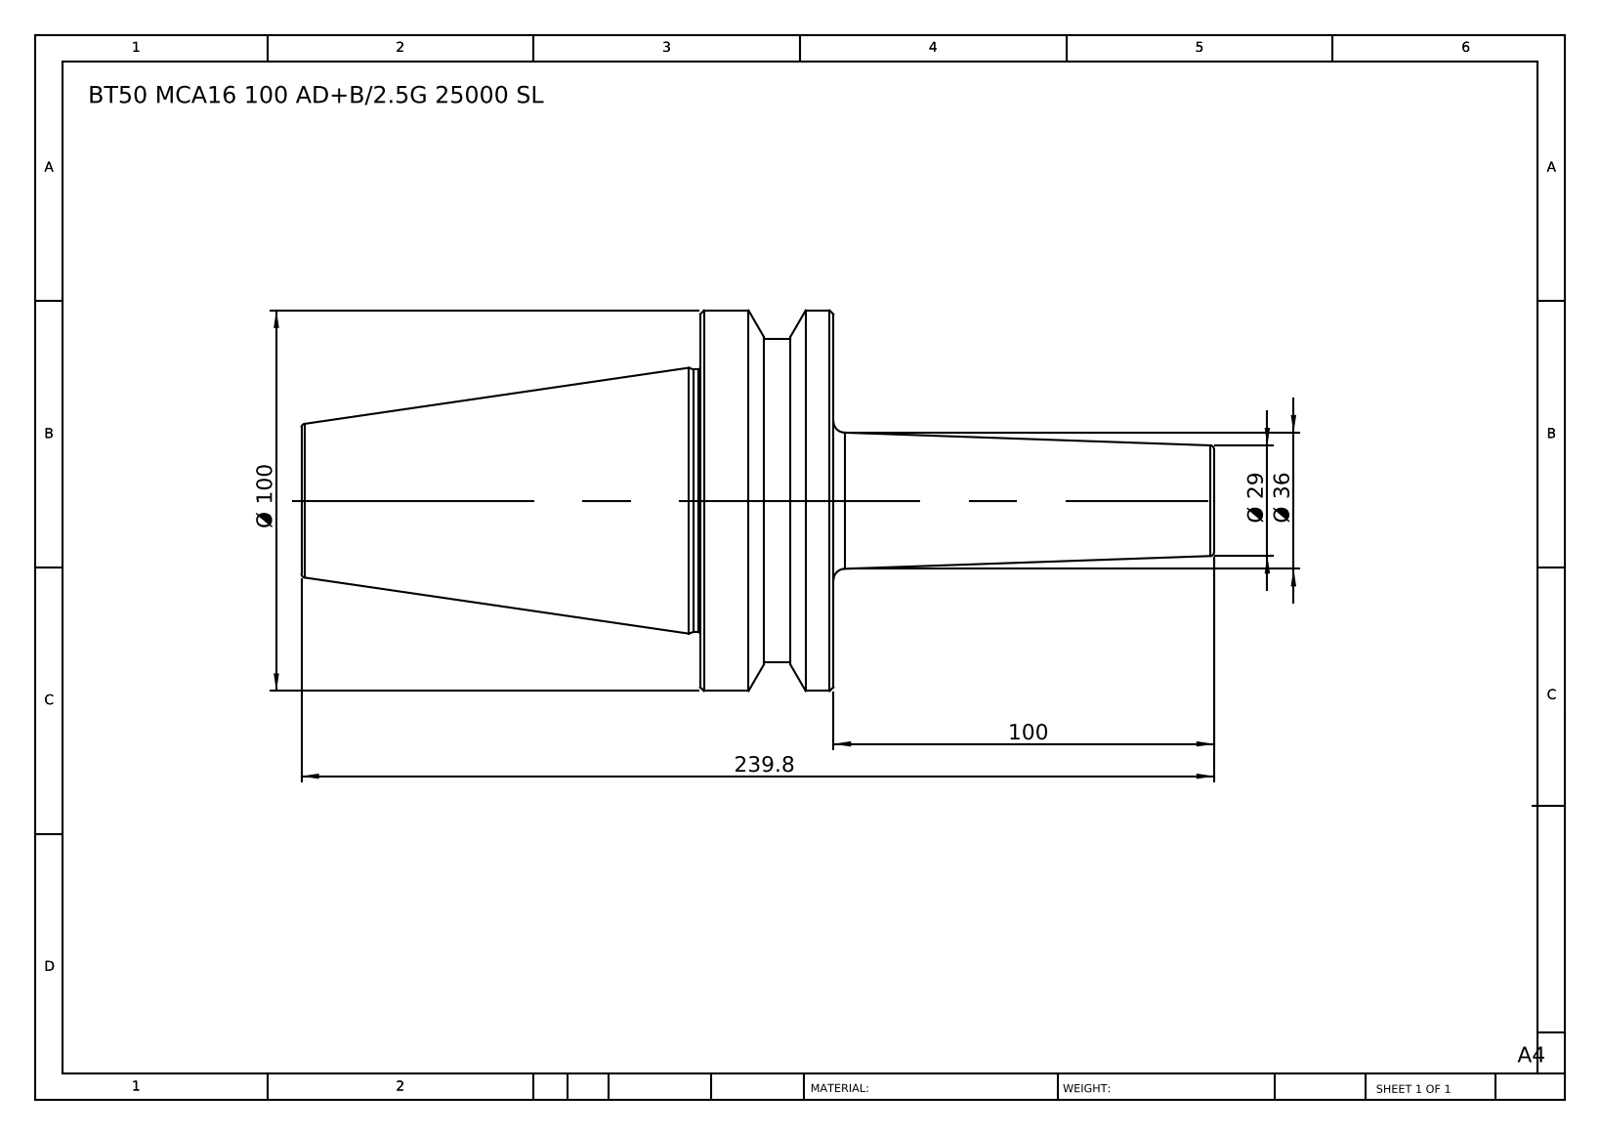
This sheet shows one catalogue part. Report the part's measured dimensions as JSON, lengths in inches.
{"part_name": "BT50 MCA16 100 AD+B-2.5G 25000 SL", "step_written_by": "SolidWorks 2014 (CONFIG_CONTROL_DESIGN)", "units": "inches", "bodies": {"solids": 1, "faces": 36, "planar": 6, "cylindrical": 8, "other": 22}, "overall_size": [9.441, 3.937, 3.937], "volume_in3": 36.22, "surface_area_in2": 83.79, "round_bosses_or_shafts": [[3.937, 1], [3.346, 1], [2.717, 1]], "face_to_face_distances": [1.378, 5.504, 4.126, 3.937, 5.315, 9.441, 4.382, 0.445, 0.933, 5.059]}
